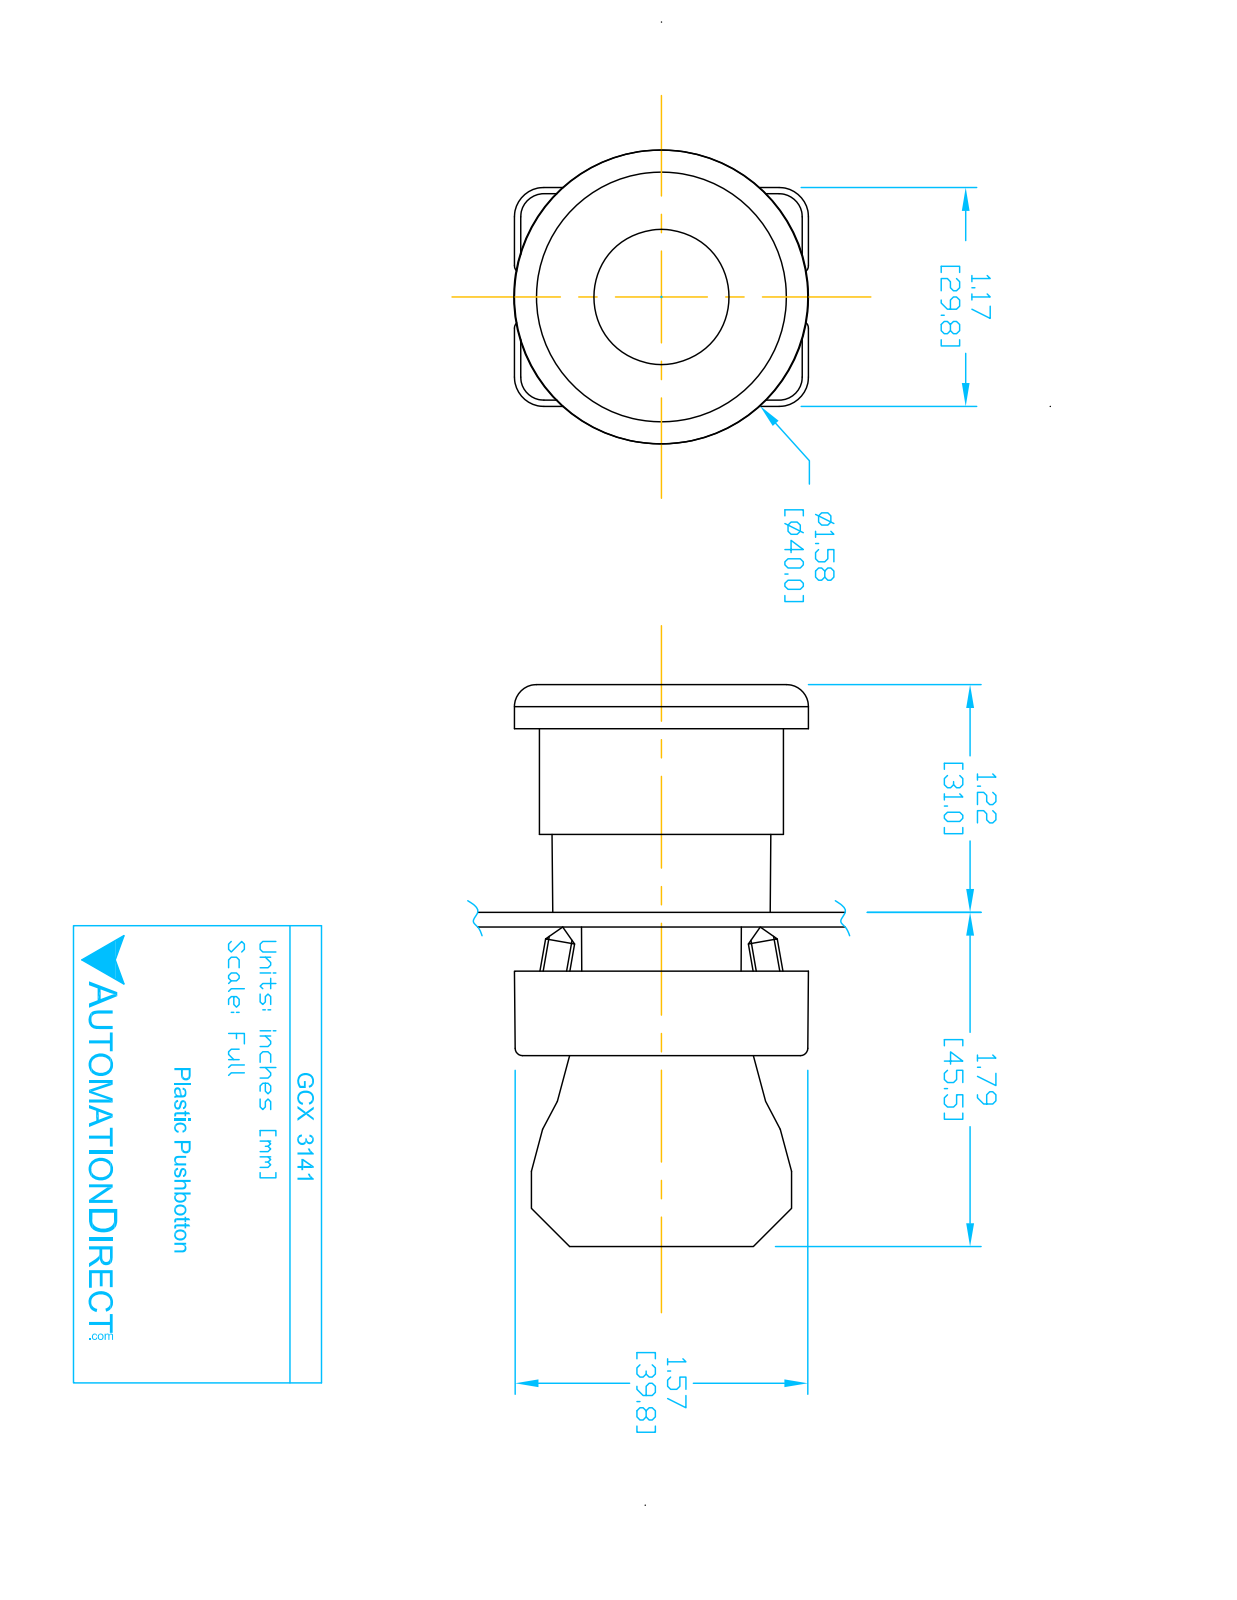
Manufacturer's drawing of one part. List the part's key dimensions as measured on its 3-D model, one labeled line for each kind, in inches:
Part name (STEP PRODUCT): ECX3029-2; GCX3141; GCX3141 OPERATOR; ecx1030
STEP written by: SolidWorks 2016 (AUTOMOTIVE_DESIGN)
Units: inches
Bodies: 7 solids, 399 faces (230 planar, 138 cylindrical, 31 other)
Overall size (bounding box): 2.944 × 1.581 × 1.575
Volume: 1.821 in³ · Surface area: 34.08 in²
Round holes (diameter × count): ⌀0.079 ×2, ⌀0.124 ×2, ⌀0.13 ×2, ⌀0.087 ×1, ⌀0.197 ×1, ⌀0.591 ×1, ⌀0.878 ×1, ⌀0.888 ×1, ⌀1.024 ×1, ⌀1.181 ×1
Round bosses / shafts (diameter × count): ⌀0.157 ×2, ⌀1.299 ×1, ⌀1.175 ×1, ⌀0.945 ×1, ⌀0.856 ×1, ⌀0.78 ×1, ⌀0.591 ×1
Partial cylindrical surfaces — rounded edges, fillets, slot ends (radius × count): R0.059 ×24, R0.041 ×12, R0.124 ×12, R0.157 ×12, R0.039 ×4, R0.128 ×2, R0.02 ×1, R0.063 ×1
Main face-to-face distances: 1.921, 0.579, 0.033, 1.763, 0.157, 0.031, 0.72, 1.043, 1.2, 0.689
Hole centre spacings: 0.236, 0.544, 0.472, 0.49
